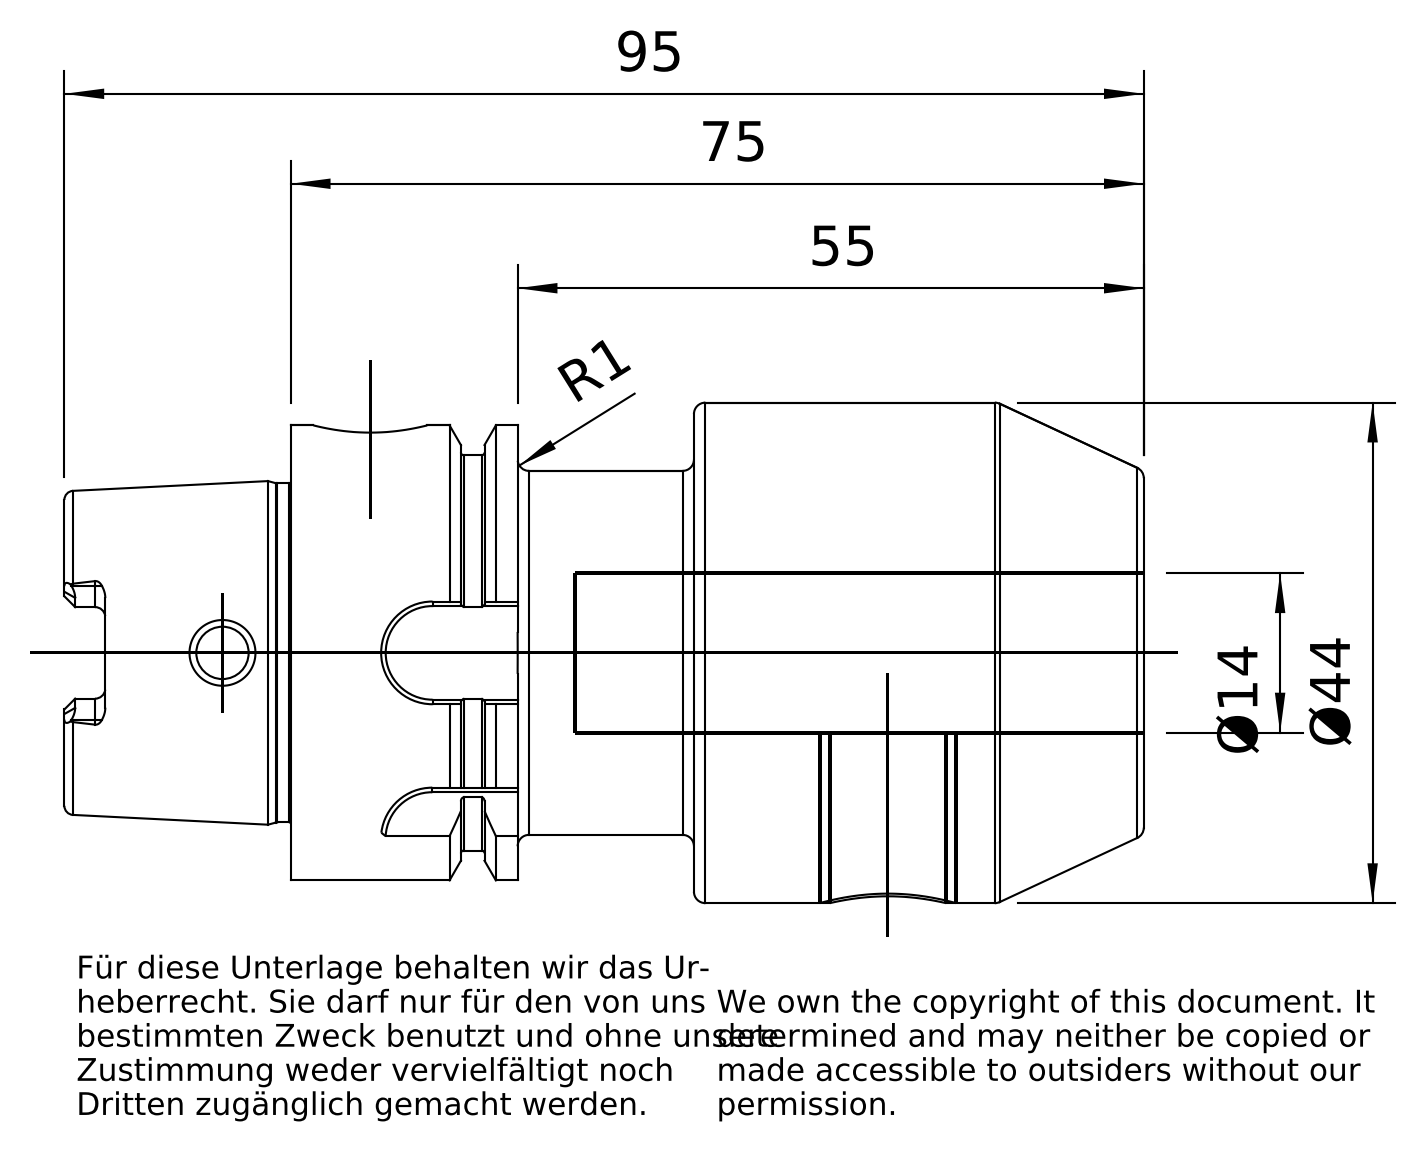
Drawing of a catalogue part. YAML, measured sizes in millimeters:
part_name: "A40-00014"
step_written_by: "PRO/ENGINEER BY PARAMETRIC TECHNOLOGY CORPORATION, 2010430 (CONFIG_CONTROL_DESIGN)"
units: millimeters
bodies: {solids: 1, faces: 198, planar: 62, cylindrical: 56, other: 80}
overall_size: [94.9, 44, 44]
volume: 82893
surface_area: 20377
round_holes:
  - {diameter: 10.2, count: 2}
  - {diameter: 12, count: 2}
  - {diameter: 4.6, count: 1}
  - {diameter: 10, count: 1}
  - {diameter: 12.22, count: 1}
  - {diameter: 12.5, count: 1}
  - {diameter: 14, count: 1}
  - {diameter: 21.04, count: 1}
  - {diameter: 25.57, count: 1}
round_bosses_or_shafts:
  - {diameter: 44, count: 1}
  - {diameter: 40, count: 1}
  - {diameter: 34.75, count: 1}
  - {diameter: 32, count: 1}
  - {diameter: 29.81, count: 1}
partial_cylinders:
  - {radius: 0.9, count: 6}
  - {radius: 1.88, count: 4}
  - {radius: 4.5, count: 3}
  - {radius: 4.51, count: 1}
face_to_face_distances: [39.55, 35.45, 75, 19.95, 15.5, 55.05, 7.95, 12, 27.5, 67.05]
hole_center_spacings: [45.5]
